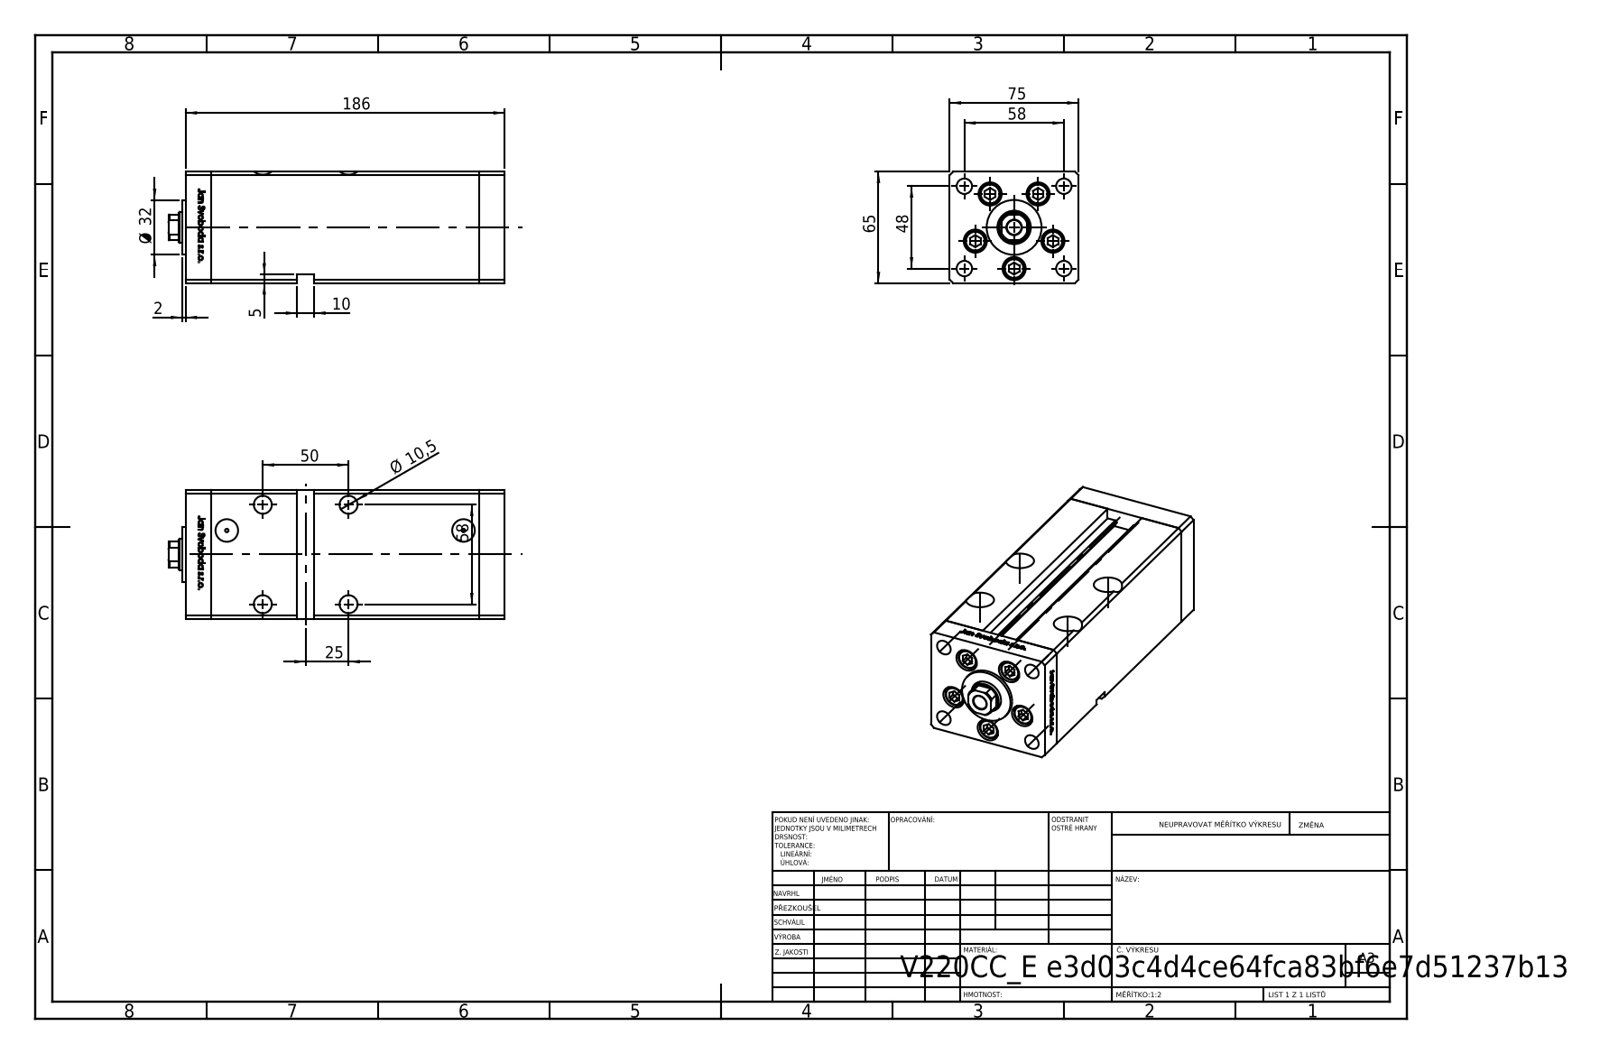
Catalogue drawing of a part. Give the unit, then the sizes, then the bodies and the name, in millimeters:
Units: millimetres
Overall size (bounding box): 196 × 75 × 65
Round holes (diameter × count): ⌀9 ×9, ⌀13.5 ×5, ⌀10.5 ×4, ⌀16.5 ×4, ⌀2 ×2, ⌀13.16 ×2, ⌀8.5 ×1, ⌀18 ×1, ⌀19.5 ×1
Round bosses / shafts (diameter × count): ⌀12.5 ×5, ⌀8 ×5, ⌀32 ×1
Partial cylindrical surfaces — rounded edges, fillets, slot ends (radius × count): R0.93 ×2, R8.5 ×1
Main face-to-face distances: 75, 65, 15, 156, 171, 186, 28, 54.5, 10.5, 26.25
Hole centre spacings: 24, 37.64, 58, 15.67, 17.22, 27.71, 28.83, 29
Volume: 769 603 mm³ · Surface area: 146 638 mm²
Bodies: 14 solids, 1212 faces (473 planar, 165 cylindrical, 574 other)
Part name (STEP PRODUCT): V220C_E MIDDLE; V220C_FRONT_E; ALLEN BOLT; V220C_VC_E (+1 more)
STEP written by: SolidWorks 2019 (CONFIG_CONTROL_DESIGN)
